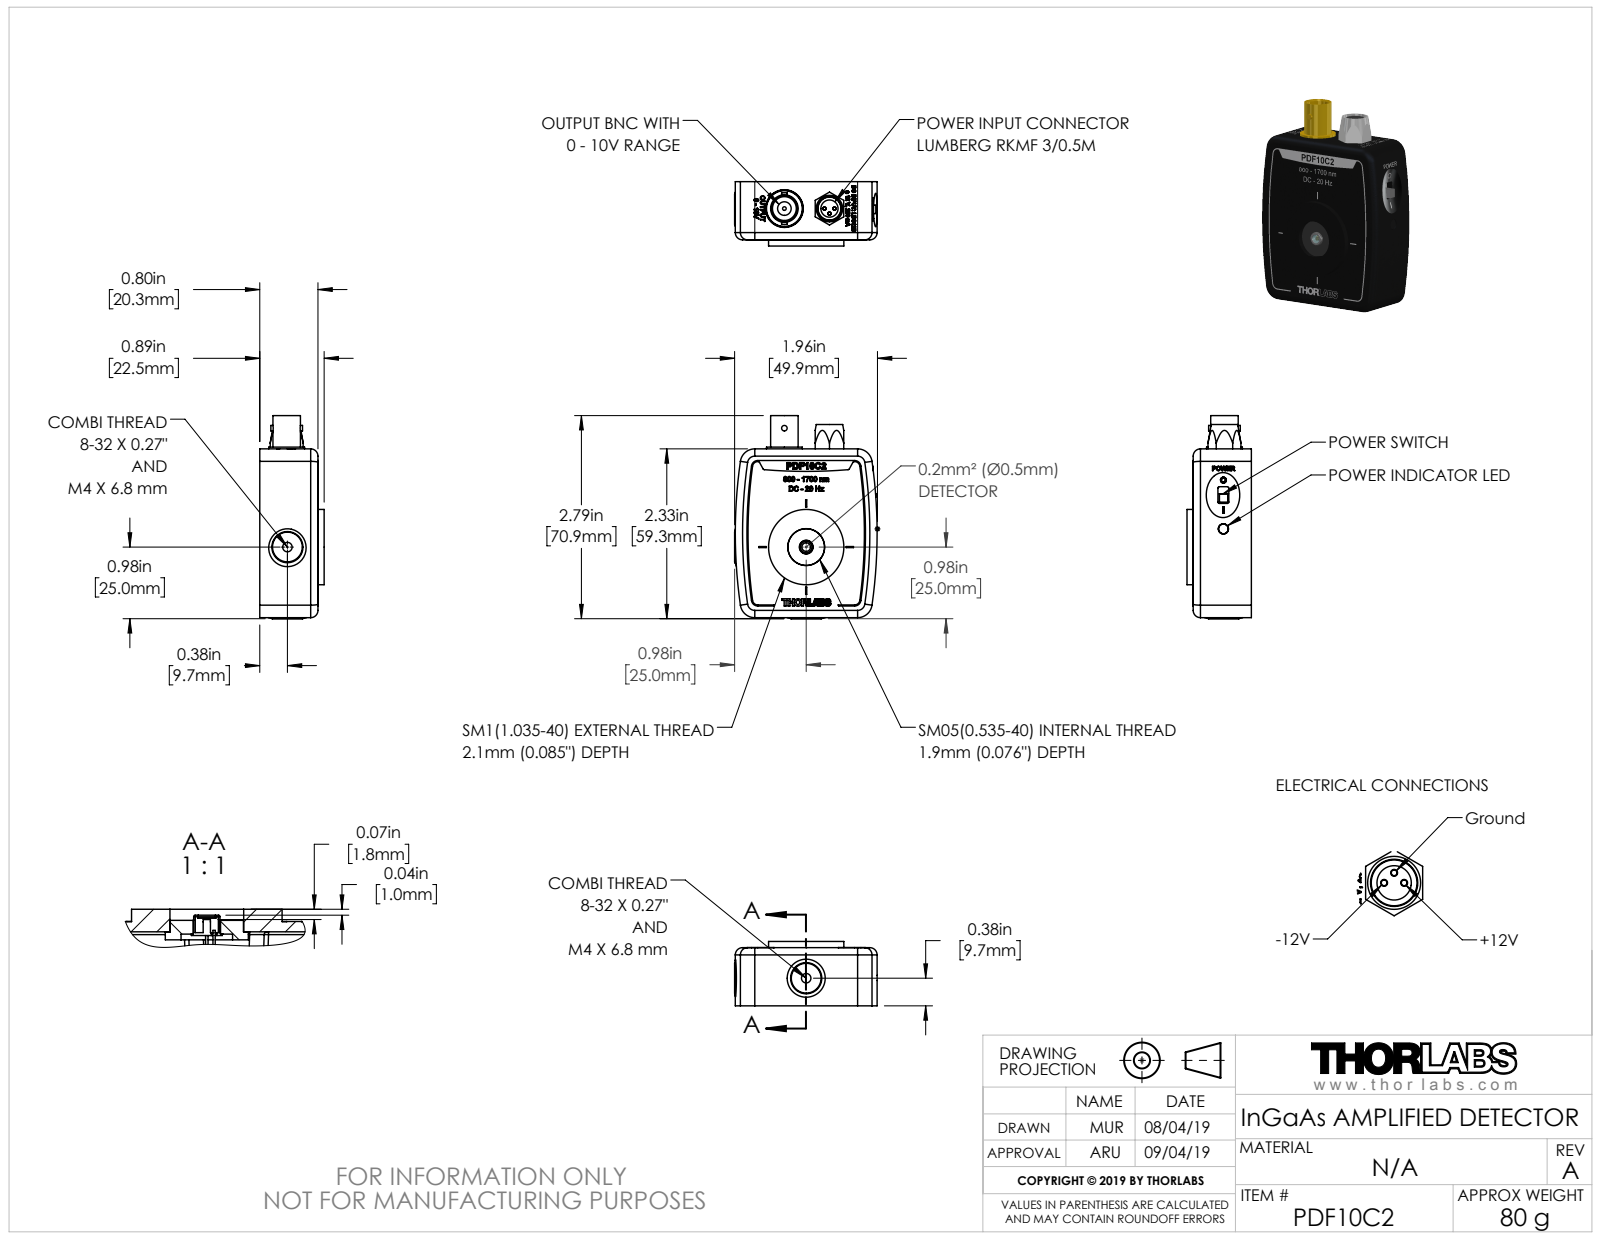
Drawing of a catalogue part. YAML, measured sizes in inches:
part_name: "21.11.02_PDF10C2"
step_written_by: "SolidWorks 2019 (AUTOMOTIVE_DESIGN)"
units: inches
bodies: {solids: 0, faces: 4127, planar: 2327, cylindrical: 192, other: 1608}
overall_size: [2.791, 1.959, 0.885]
round_holes:
  - {diameter: 0.07, count: 7}
  - {diameter: 0.039, count: 3}
  - {diameter: 0.04, count: 3}
  - {diameter: 0.13, count: 2}
  - {diameter: 0.015, count: 1}
  - {diameter: 0.035, count: 1}
  - {diameter: 0.05, count: 1}
  - {diameter: 0.094, count: 1}
  - {diameter: 0.115, count: 1}
  - {diameter: 0.118, count: 1}
  - {diameter: 0.14, count: 1}
  - {diameter: 0.159, count: 1}
round_bosses_or_shafts:
  - {diameter: 0.197, count: 4}
  - {diameter: 0.086, count: 4}
  - {diameter: 0.017, count: 3}
  - {diameter: 1.035, count: 1}
  - {diameter: 0.571, count: 1}
  - {diameter: 0.504, count: 1}
  - {diameter: 0.492, count: 1}
  - {diameter: 0.37, count: 1}
partial_cylinders:
  - {radius: 0.02, count: 18}
  - {radius: 0.03, count: 8}
  - {radius: 0.1, count: 8}
  - {radius: 0.008, count: 4}
  - {radius: 0.022, count: 4}
  - {radius: 0.063, count: 4}
  - {radius: 0.073, count: 4}
  - {radius: 0.088, count: 4}
face_to_face_distances: [0.059, 0.726, 0.667, 0.07, 0.737, 0.796, 2.32, 0.085, 0.155, 0.822]
hole_center_spacings: [0.05, 0.069, 0.071, 0.097, 0.762, 0.78, 0.826, 1.07]
